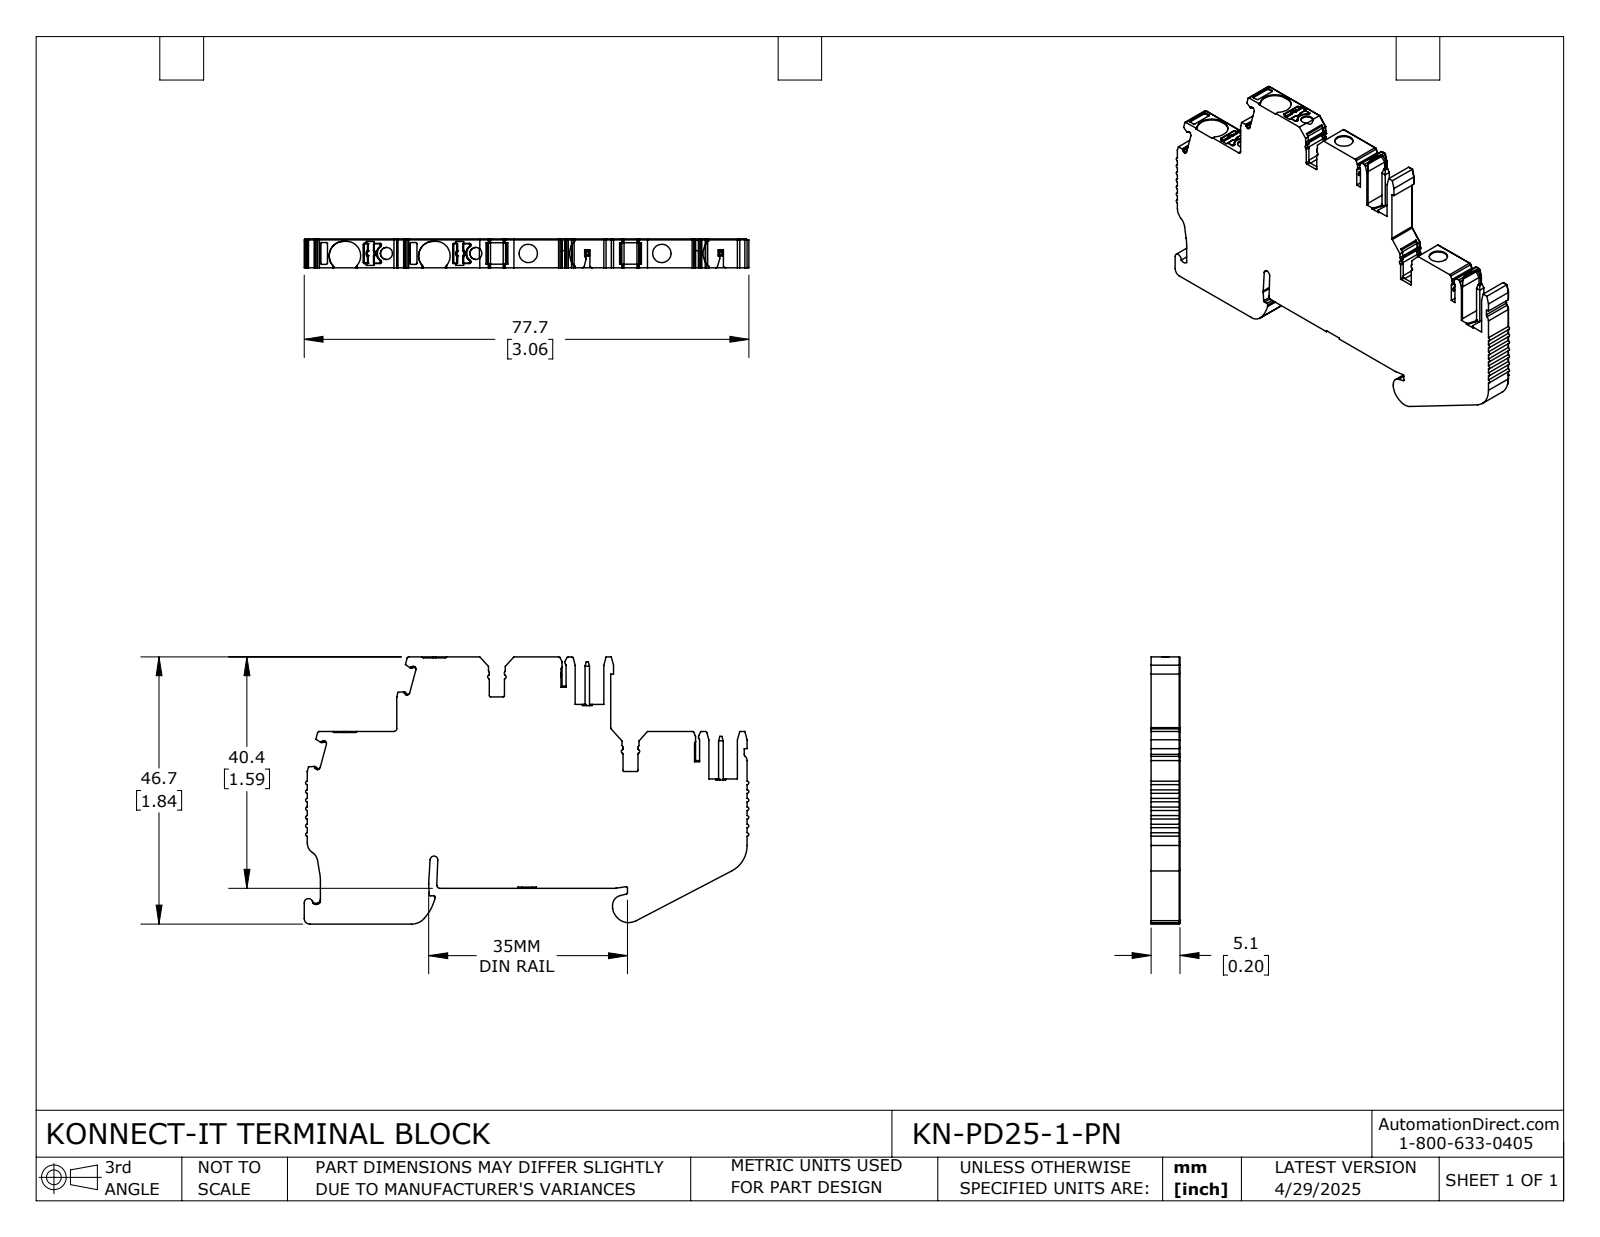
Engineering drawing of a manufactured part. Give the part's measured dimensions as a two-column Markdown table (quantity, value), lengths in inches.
| quantity | value |
| --- | --- |
| part name | KN-PD25-1-PN |
| STEP written by | SolidWorks 2024 (CONFIG_CONTROL_DESIGN) |
| units | inches |
| bodies | 1 solid, 731 faces (387 planar, 304 cylindrical, 40 other) |
| overall size | 3.057 × 1.837 × 0.199 |
| volume | 0.786 in³ |
| surface area | 10.88 in² |
| round holes (diameter × count) | 0.083 × 2, 0.126 × 2 |
| partial cylindrical surfaces (radius × count) | 0.008 × 58, 0.012 × 48, 0.004 × 23, 0.016 × 16, 0.02 × 16, 0.006 × 8, 0.024 × 6, 0.006 × 4 |
| main face-to-face distances | 0.199, 0.512, 0.919, 0.246, 1.324, 1.078, 1.837, 1.591, 0.205, 1.07 |
| hole center spacings | 0.36, 0.615, 0.919, 0.975, 1.278, 1.893 |
